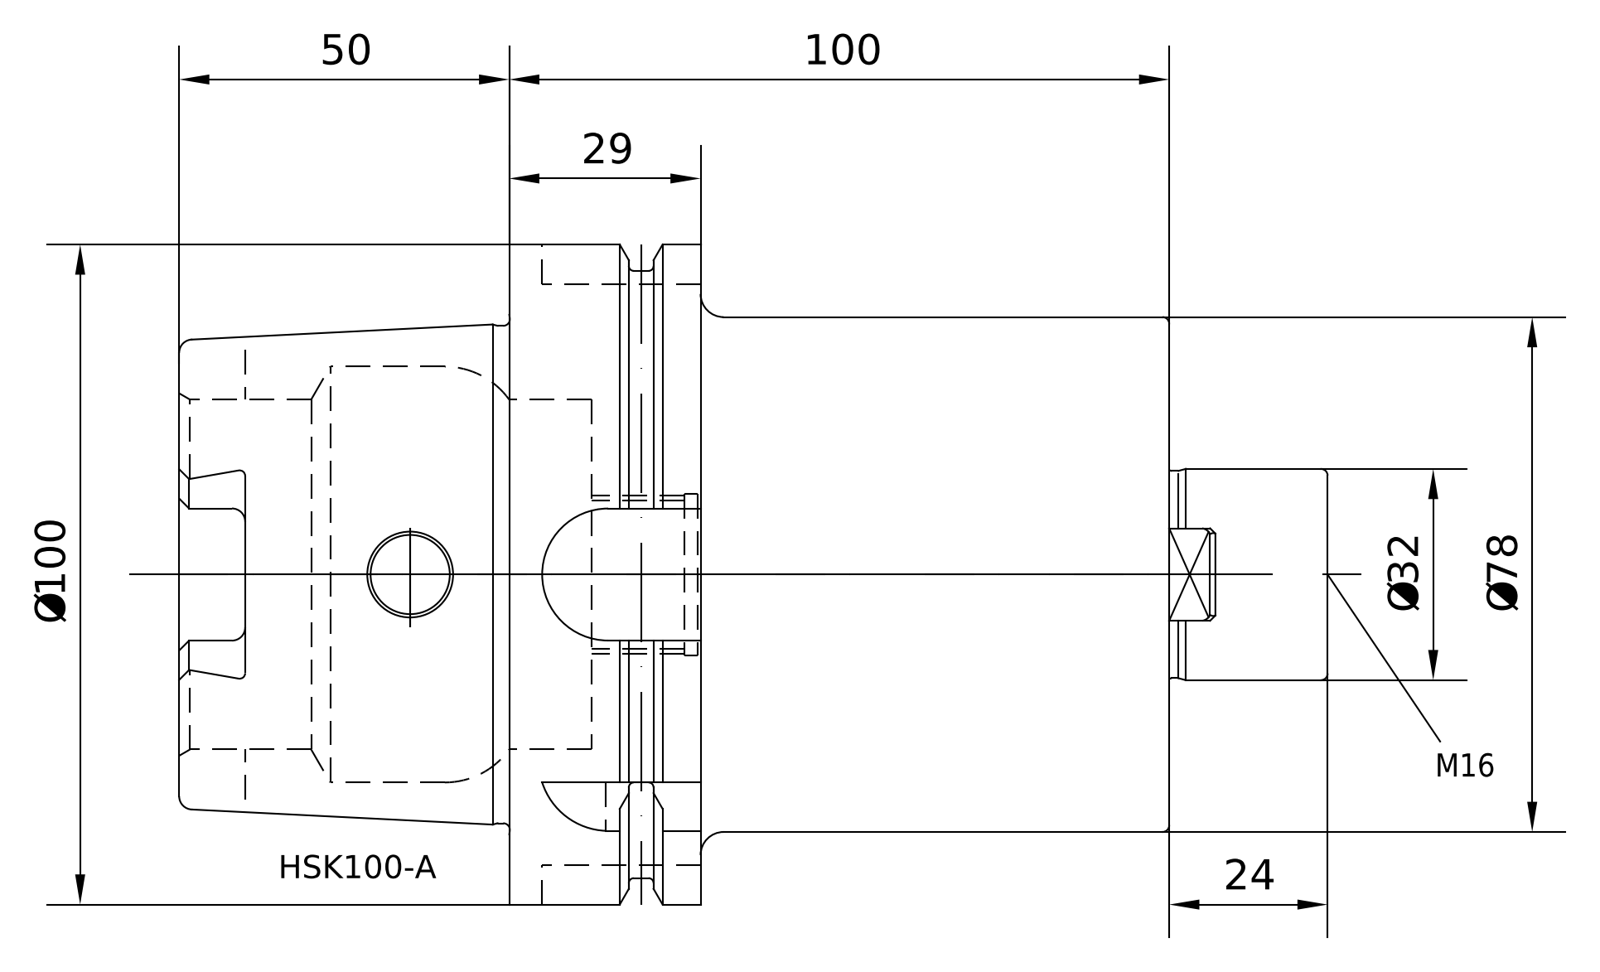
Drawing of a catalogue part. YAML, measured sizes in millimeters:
part_name: "A100-051-32"
step_written_by: "PRO/ENGINEER BY PARAMETRIC TECHNOLOGY CORPORATION, 2010430 (CONFIG_CONTROL_DESIGN)"
units: millimeters
bodies: {solids: 1, faces: 191, planar: 61, cylindrical: 55, other: 75}
overall_size: [174, 100, 100]
volume: 609730
surface_area: 73659
round_holes:
  - {diameter: 10, count: 1}
  - {diameter: 12, count: 1}
  - {diameter: 14, count: 1}
  - {diameter: 16, count: 1}
  - {diameter: 22.5, count: 1}
  - {diameter: 24, count: 1}
  - {diameter: 24.32, count: 1}
  - {diameter: 24.5, count: 1}
  - {diameter: 53, count: 1}
  - {diameter: 63, count: 1}
round_bosses_or_shafts:
  - {diameter: 100, count: 1}
  - {diameter: 92, count: 1}
  - {diameter: 78, count: 1}
  - {diameter: 75.36, count: 1}
  - {diameter: 32, count: 1}
partial_cylinders:
  - {radius: 2, count: 6}
  - {radius: 5, count: 4}
  - {radius: 8, count: 1}
  - {radius: 10, count: 1}
  - {radius: 11, count: 1}
face_to_face_distances: [100, 29, 71, 12.5, 16.5, 87.5, 50, 62.5, 79, 150]
